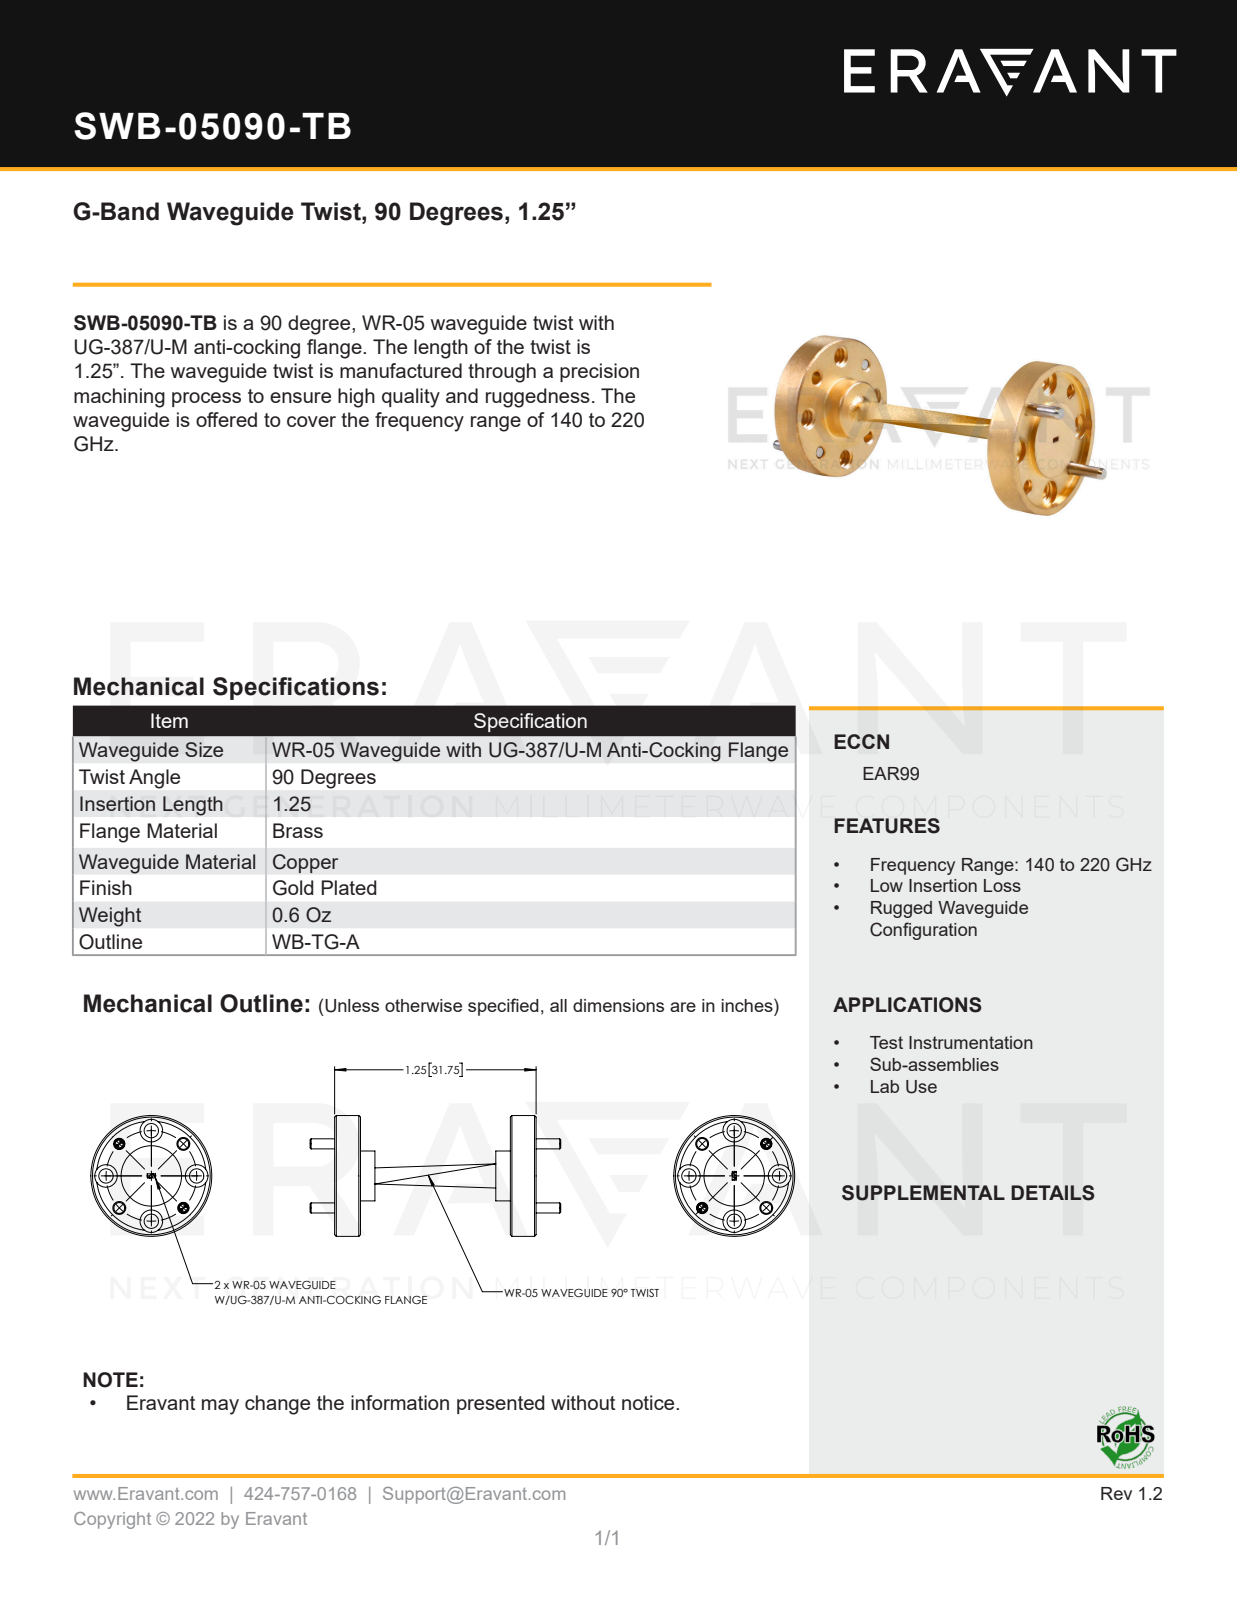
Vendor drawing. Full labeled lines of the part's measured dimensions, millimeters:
Part name (STEP PRODUCT): SWB-05090-TB
STEP written by: SolidWorks 2021 (CONFIG_CONTROL_DESIGN)
Units: millimetres
Bodies: 5 solids, 156 faces (36 planar, 76 cylindrical, 44 other)
Overall size (bounding box): 39.5 × 19.1 × 19.1
Volume: 2 330 mm³ · Surface area: 2 418 mm²
Round holes (diameter × count): ⌀2.3 ×4, ⌀3.6 ×4, ⌀1.5 ×2, ⌀1.7 ×2, ⌀17.3 ×1
Round bosses / shafts (diameter × count): ⌀1.6 ×2, ⌀19.1 ×1, ⌀9.5 ×1, ⌀7.9 ×1
Main face-to-face distances: 3.6, 27.2, 0.5, 4.1, 27.7, 31.2, 23.6, 30.7, 31.8, 6.4
Hole centre spacings: 5.5, 7.1, 10.1, 13.2, 14.3
